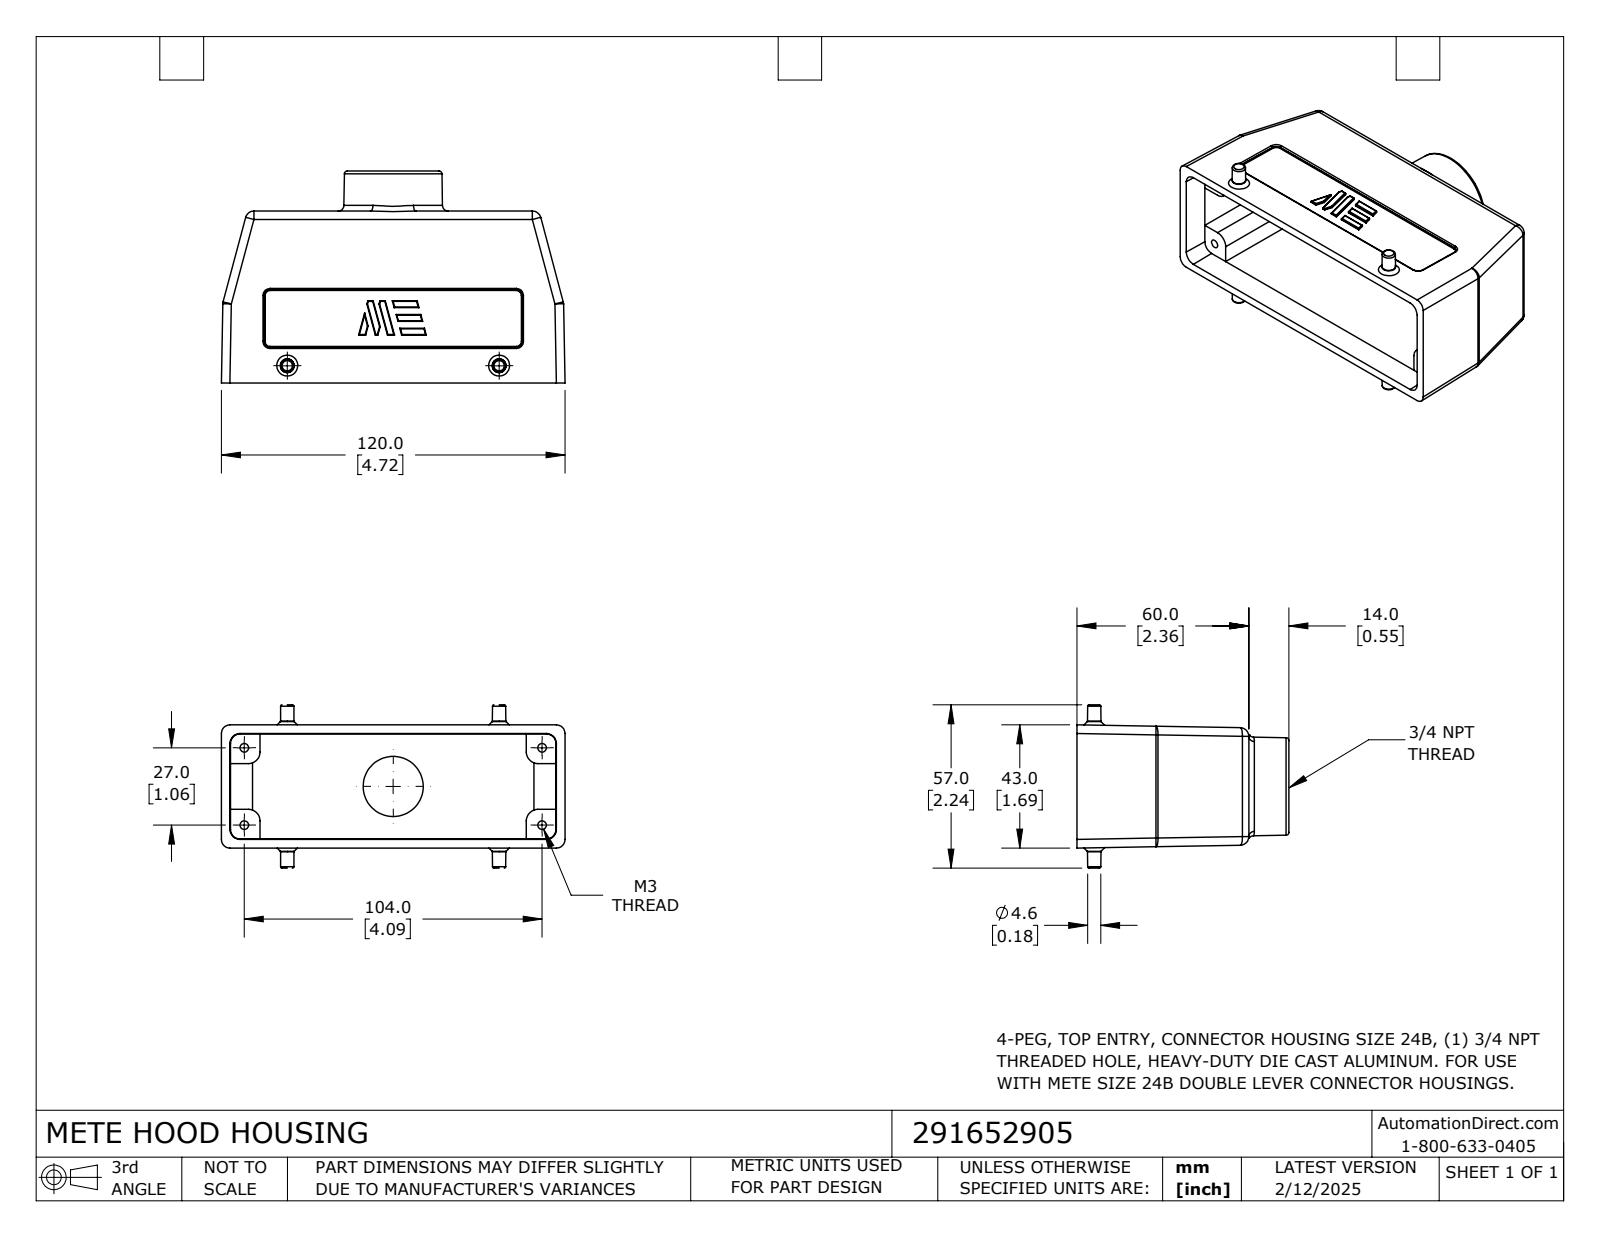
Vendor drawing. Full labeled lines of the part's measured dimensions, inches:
Part name (STEP PRODUCT): 291652905
STEP written by: SolidWorks 2024 (CONFIG_CONTROL_DESIGN)
Units: inches
Bodies: 1 solid, 297 faces (118 planar, 108 cylindrical, 71 other)
Overall size (bounding box): 4.724 × 2.913 × 2.244
Volume: 4.95 in³ · Surface area: 71.94 in²
Round holes (diameter × count): ⌀0.118 ×4, ⌀0.827 ×1, ⌀1.063 ×1
Partial cylindrical surfaces — rounded edges, fillets, slot ends (radius × count): R0.008 ×46, R0.118 ×12, R0.02 ×8, R0.079 ×8, R0.157 ×4, R0.114 ×2
Main face-to-face distances: 1.444, 0.118, 0.031, 0.197, 0.087, 0.407, 2.362, 2.165, 1.037, 3.661
Hole centre spacings: 2.115, 1.063, 4.094, 4.23
